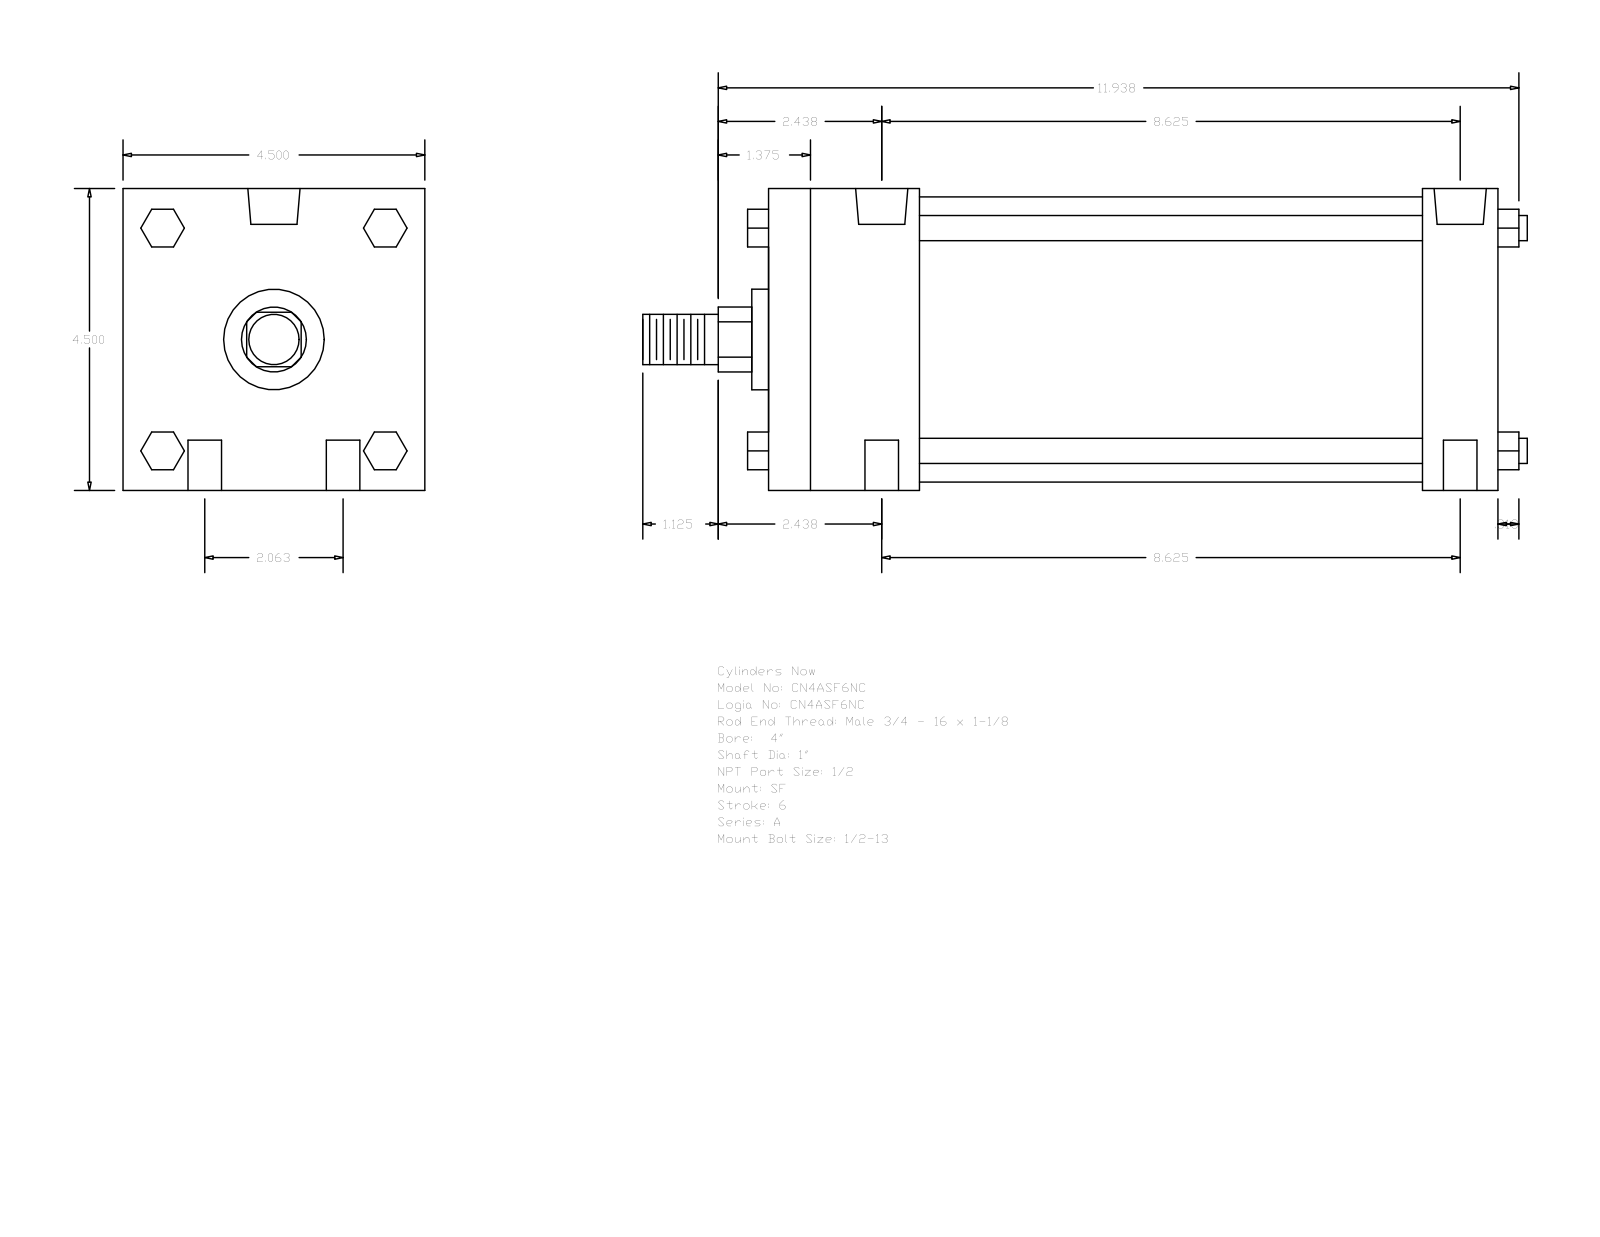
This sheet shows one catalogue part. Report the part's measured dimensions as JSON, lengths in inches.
{"part_name": "A_SF__0400_1", "step_written_by": "GSSL Pune (CONFIG_CONTROL_DESIGN)", "units": "inches", "bodies": {"solids": 0, "faces": 124, "planar": 94, "cylindrical": 30, "other": 0}, "overall_size": [13.187, 4.5, 4.5], "round_holes": [[0.5, 4], [0.344, 2], [0.778, 2]], "round_bosses_or_shafts": [[0.375, 4], [4.25, 1], [1.5, 1], [1, 1], [0.75, 1]], "partial_cylinders_radius": [[0.484, 1]], "face_to_face_distances": [4.5, 10.875, 1.125, 9.75, 2.25, 7.5, 8.625, 0.563, 1.66, 2.875], "hole_center_spacings": [1.031, 8.687, 8.625, 2.062, 8.868, 8.375]}
